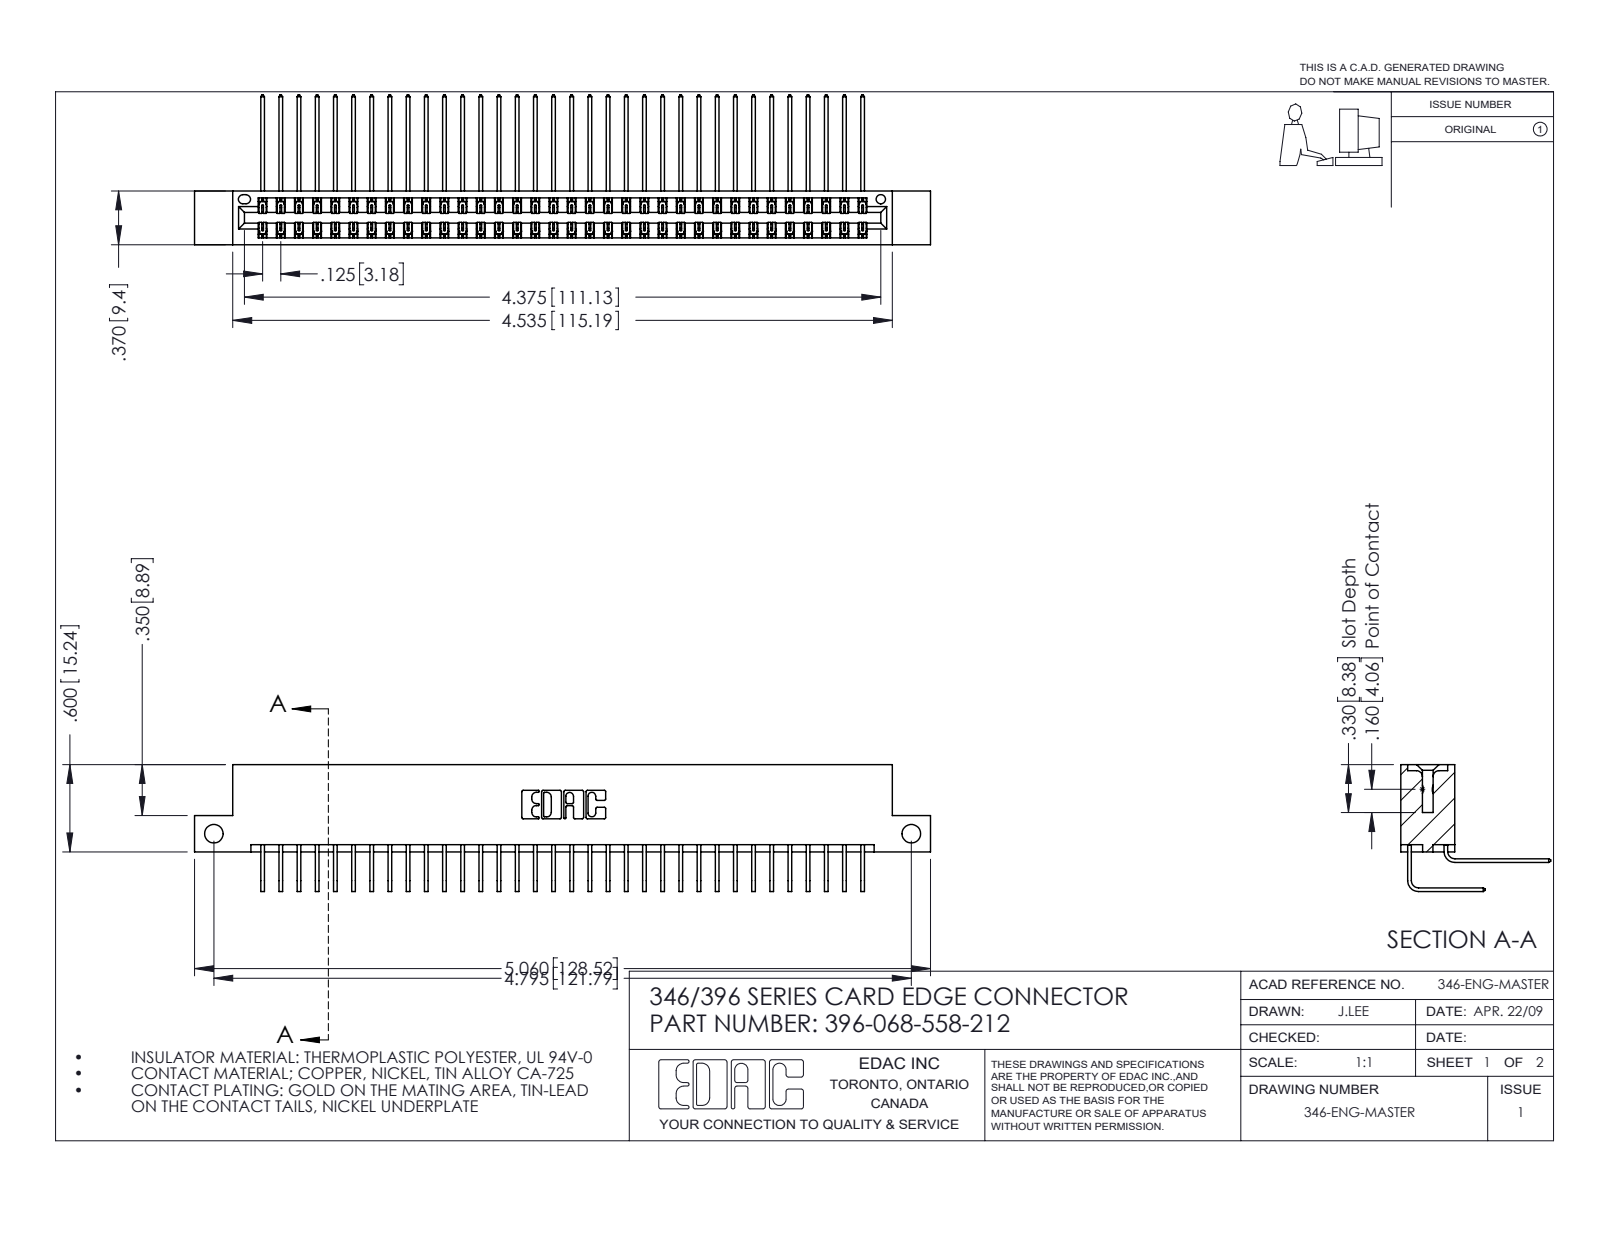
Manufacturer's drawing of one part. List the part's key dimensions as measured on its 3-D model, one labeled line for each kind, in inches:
Part name (STEP PRODUCT): 345-292-001_558 Tail - 2; 346 Part_Flush Mounting Lugs - Side Mount; 345-292-001_558 559 Tail - 1; 396-068-558-212
STEP written by: SolidWorks 2016 (CONFIG_CONTROL_DESIGN)
Units: inches
Bodies: 69 solids, 3794 faces (2592 planar, 1202 cylindrical, 0 other)
Overall size (bounding box): 5.06 × 1.03 × 0.873
Volume: 0.78 in³ · Surface area: 29.73 in²
Round holes (diameter × count): ⌀0.128 ×2, ⌀0.064 ×1
Partial cylindrical surfaces — rounded edges, fillets, slot ends (radius × count): R0.006 ×102, R0.01 ×22, R0.007 ×6, R0.031 ×6, R0.026 ×3, R0.014 ×2, R0.022 ×2, R0.024 ×2
Main face-to-face distances: 0.322, 0.048, 0.025, 0.25, 0.37, 0.298, 0.072, 0.275, 0.148, 0.222
Hole centre spacings: 4.795
